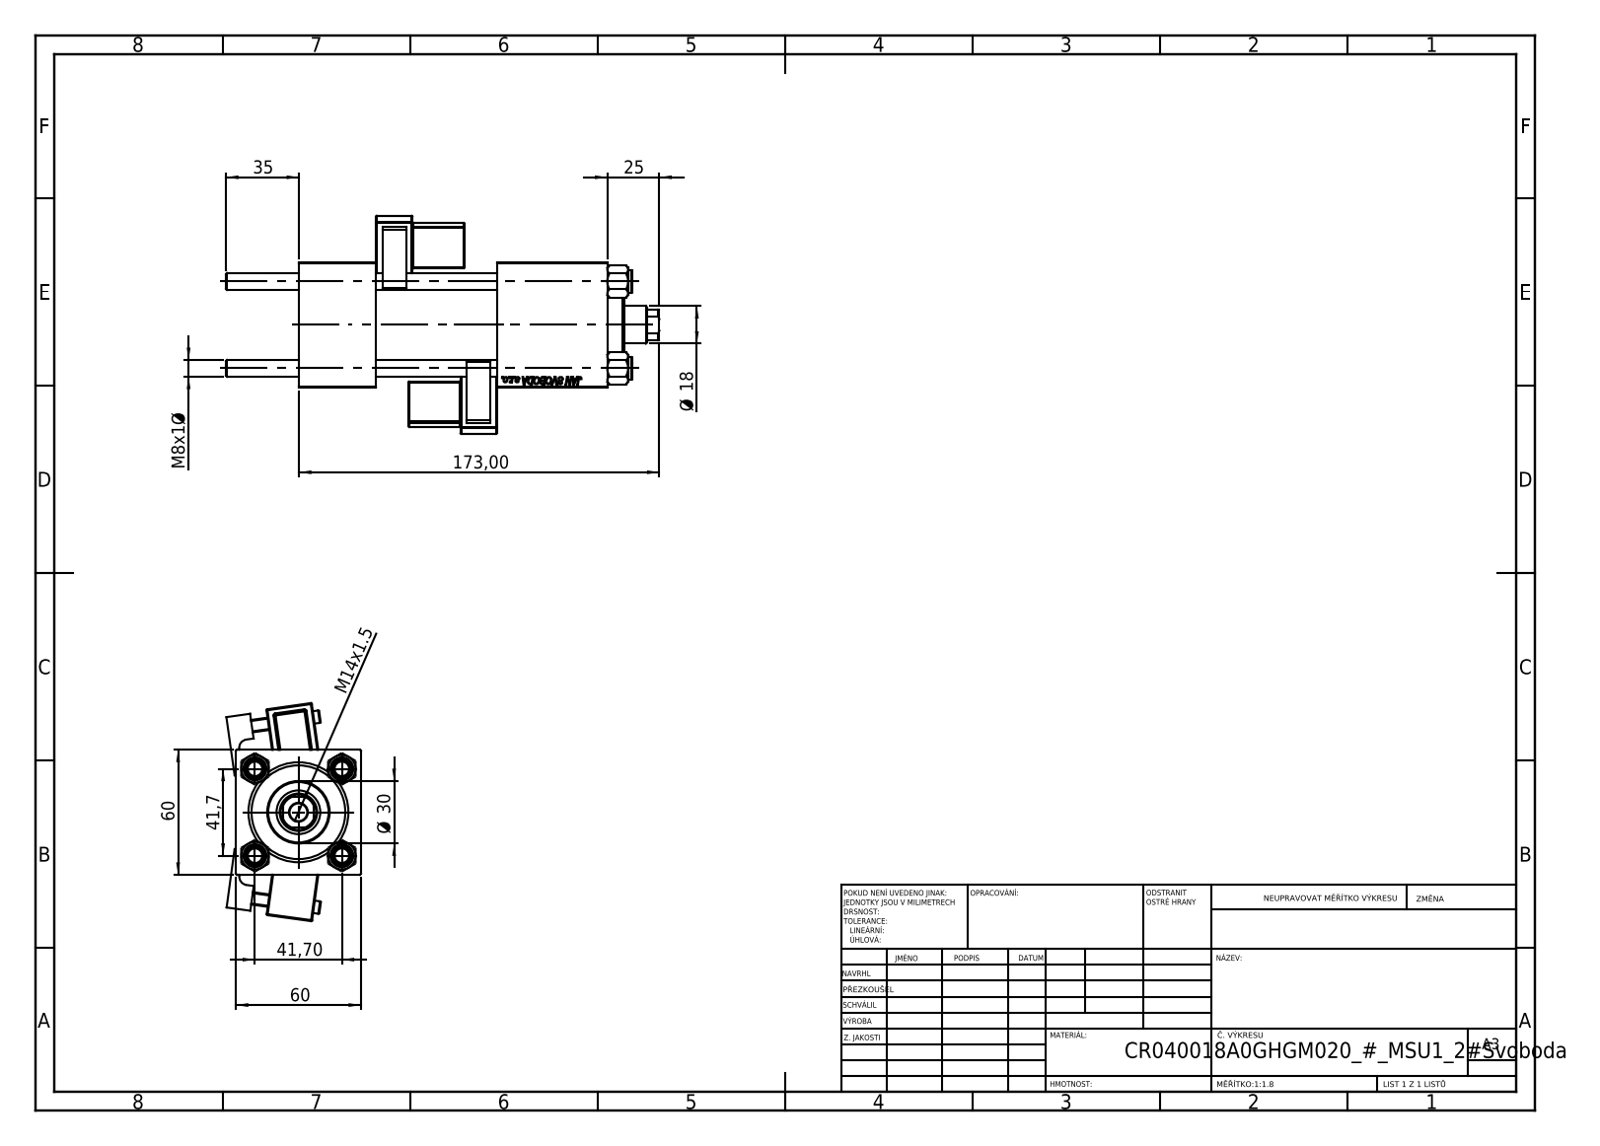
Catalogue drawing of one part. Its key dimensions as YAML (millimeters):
part_name: "V215CR_MSU; V215_VC_A; V215CR_VCP; CR025_012_A_0_G_A_G_M_020_+#_##_TYCINKA (+2 more)"
step_written_by: "SolidWorks 2019 (CONFIG_CONTROL_DESIGN)"
units: millimeters
bodies: {solids: 13, faces: 1289, planar: 579, cylindrical: 138, other: 572}
overall_size: [208, 104.69, 64.58]
volume: 454736
surface_area: 126093
round_holes:
  - {diameter: 8, count: 4}
  - {diameter: 7, count: 2}
  - {diameter: 16.66, count: 2}
  - {diameter: 24, count: 2}
  - {diameter: 8.5, count: 1}
  - {diameter: 18, count: 1}
  - {diameter: 21, count: 1}
  - {diameter: 31, count: 1}
  - {diameter: 40, count: 1}
  - {diameter: 45, count: 1}
round_bosses_or_shafts:
  - {diameter: 11, count: 4}
  - {diameter: 6, count: 2}
  - {diameter: 46, count: 1}
  - {diameter: 30, count: 1}
partial_cylinders:
  - {radius: 0.5, count: 48}
  - {radius: 1, count: 2}
  - {radius: 2.5, count: 2}
  - {radius: 4, count: 2}
  - {radius: 8.5, count: 1}
face_to_face_distances: [60, 37, 58, 53, 148, 111, 95, 119.3, 82.3, 24.3]
hole_center_spacings: [29.49, 41.7, 58.97, 92.5]
